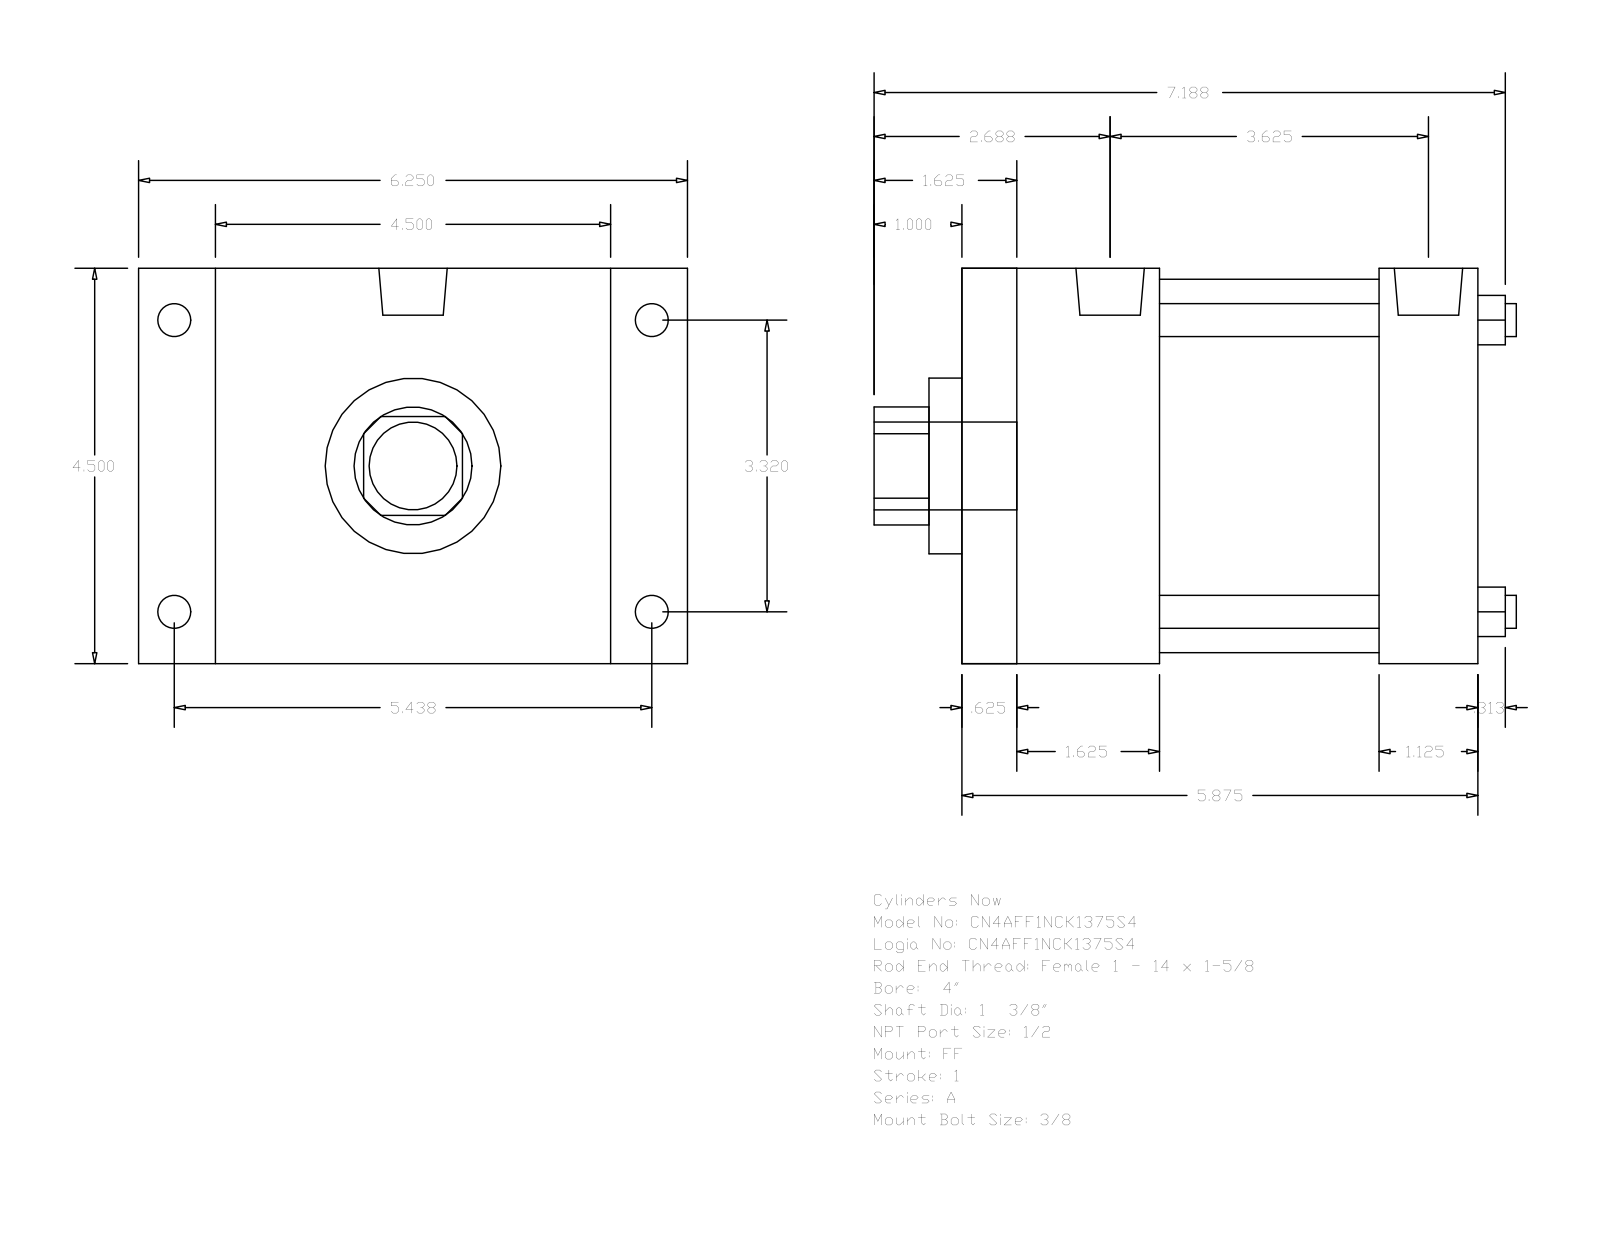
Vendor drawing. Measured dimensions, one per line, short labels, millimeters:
name: A_FF__0400_1.375
written by: GSSL Pune (CONFIG_CONTROL_DESIGN)
unit: mm
bodies: 0 solids, 92 faces (64 planar, 28 cylindrical, 0 other)
size: 185.74 × 158.75 × 114.3
holes: 4× ⌀9.53, 1× ⌀34.92, 1× ⌀50.8, 1× ⌀107.95
bosses: 4× ⌀9.53, 4× ⌀8.73, 2× ⌀19.77, 1× ⌀25.4
rounds: 1× R17.06
face distances: 114.3, 149.22, 133.35, 15.87, 28.57, 22.23, 136.53, 120.65, 104.78, 57.15
hole spacings: 59.62, 84.32, 119.25
